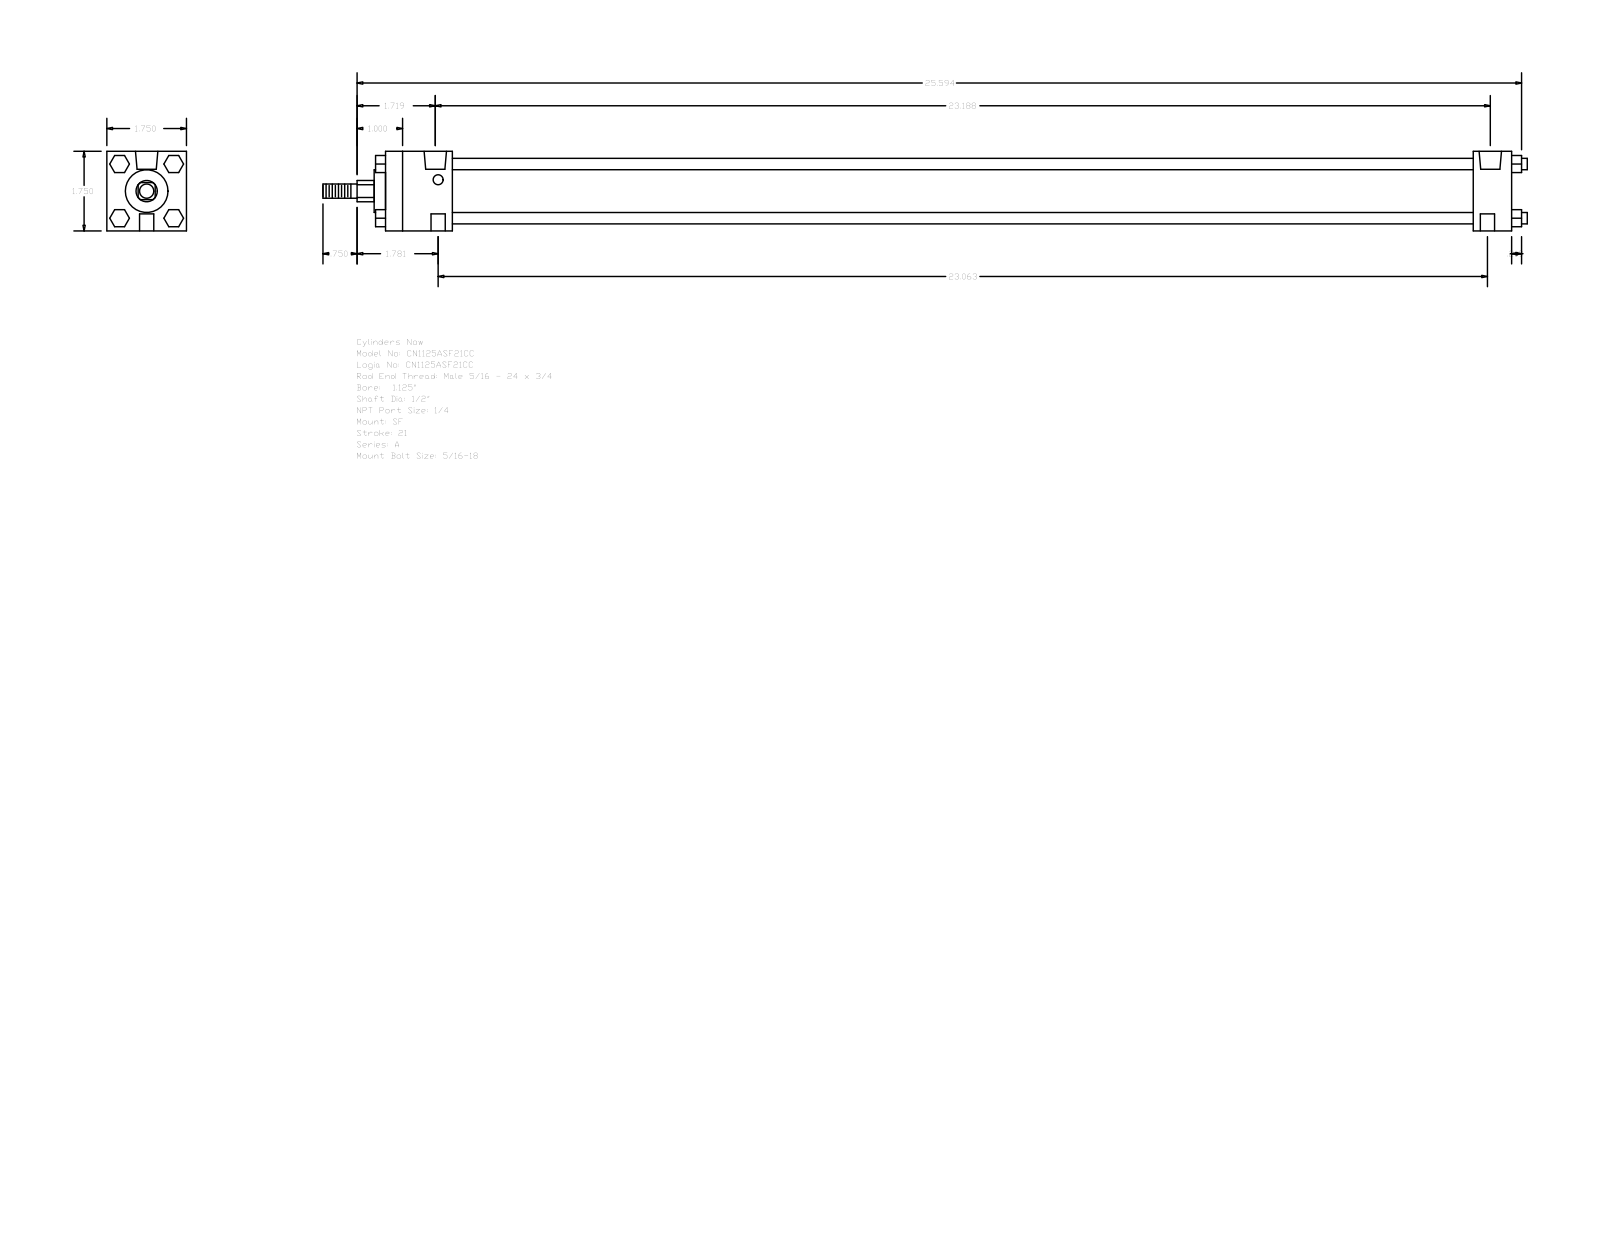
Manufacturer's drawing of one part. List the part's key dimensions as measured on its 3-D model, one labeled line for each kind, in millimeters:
Part name (STEP PRODUCT): A_SF__0112_0.5
STEP written by: GSSL Pune (CONFIG_CONTROL_DESIGN)
Units: millimetres
Bodies: 0 solids, 120 faces (92 planar, 28 cylindrical, 0 other)
Overall size (bounding box): 672.31 × 44.45 × 44.45
Round holes (diameter × count): ⌀5.56 ×2, ⌀7.94 ×2, ⌀12.49 ×2
Round bosses / shafts (diameter × count): ⌀6.35 ×4, ⌀31.88 ×1, ⌀23.81 ×1, ⌀12.7 ×1, ⌀7.94 ×1
Partial cylindrical surfaces — rounded edges, fillets, slot ends (radius × count): R5.94 ×1
Main face-to-face distances: 44.46, 628.64, 607.21, 21.43, 37.3, 569.91, 591.34, 9.53, 5.59, 5.56
Hole centre spacings: 585.79, 1.58, 1.59, 587.37, 587.38, 588.96
